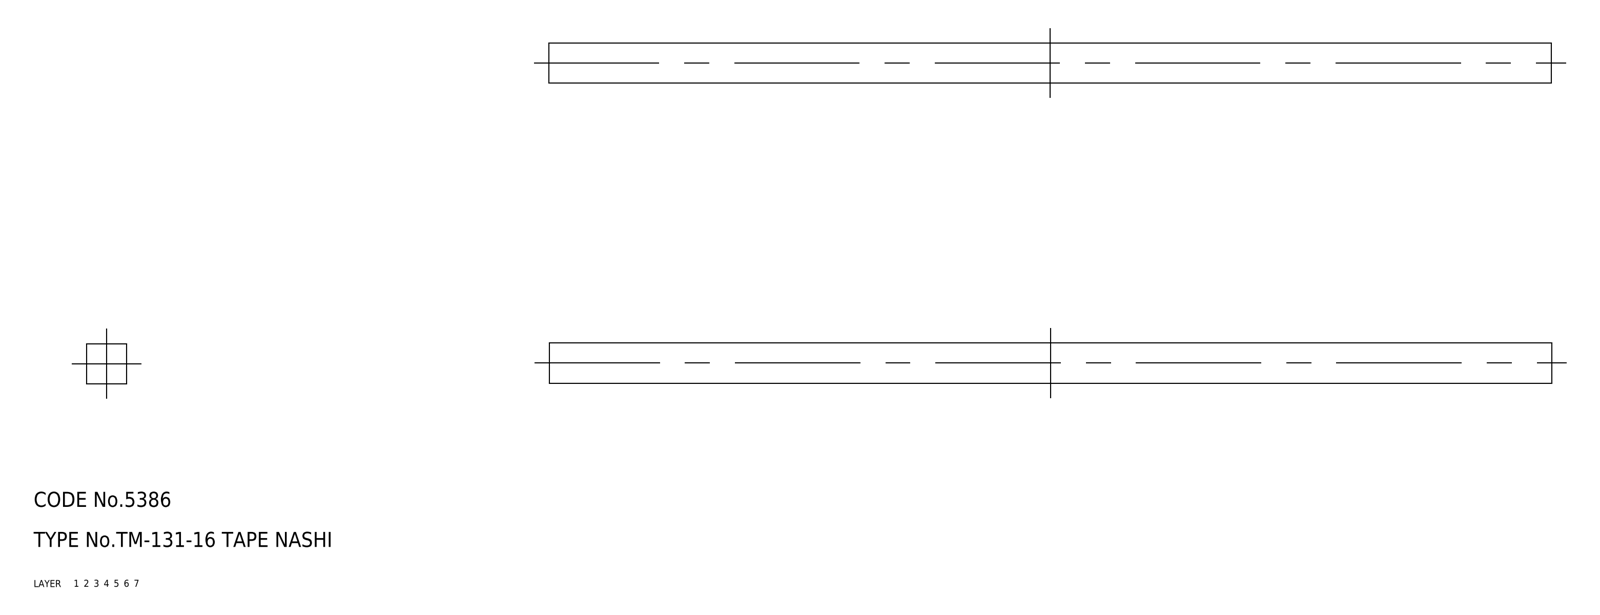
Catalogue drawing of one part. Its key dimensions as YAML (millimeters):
part_name: "rubber foam"
step_written_by: "CADfix (AUTOMOTIVE_DESIGN)"
units: millimeters
bodies: {solids: 1, faces: 6, planar: 0, cylindrical: 0, other: 6}
overall_size: [200, 8, 8]
volume: 12800
surface_area: 6528
